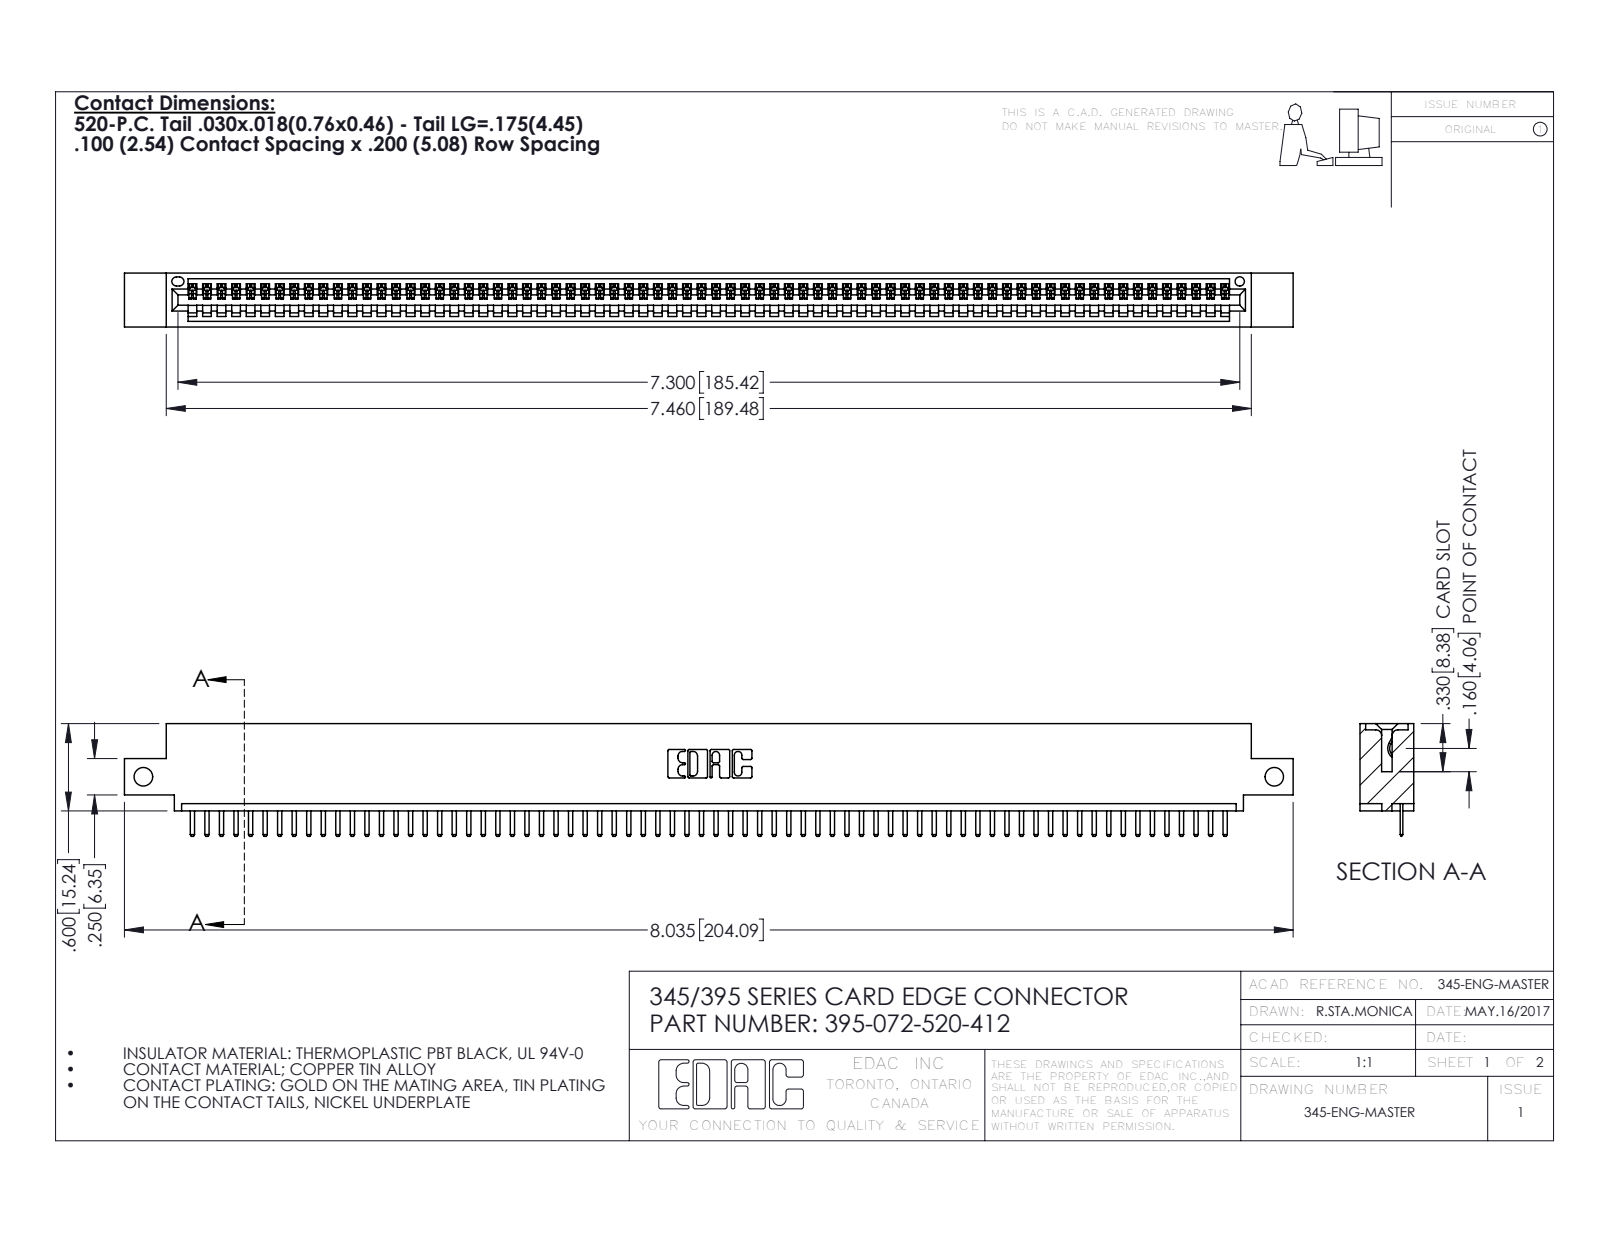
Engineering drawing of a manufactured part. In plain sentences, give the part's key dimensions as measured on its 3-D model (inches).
The part is named "345-292-001_345-293-120; 345 Part_0.110 Offset - Side Mount; 395-072-520-412". Its 3-D file was written by "SolidWorks 2016 (CONFIG_CONTROL_DESIGN)". It is 73 solids with 4594 faces: 3108 planar, 1486 cylindrical and 0 other. Overall it measures 8.035 by 0.775 by 0.37 inches. Its volume is 1.175 cubic inches and its surface area 39.17 square inches. Round holes: 2 of diameter 0.128, 1 of diameter 0.064. Partial cylindrical surfaces (rounded edges, fillets, slot ends): 146 of radius 0.01, 144 of radius 0.006, 22 of radius 0.01, 6 of radius 0.007, 6 of radius 0.031, 3 of radius 0.026, 2 of radius 0.031, 2 of radius 0.04. The main face-to-face distances are 0.298, 0.072, 0.37, 0.2, 0.098, 0.272, 0.025, 0.225, 0.072, 0.149. The hole center spacings are 7.775.
